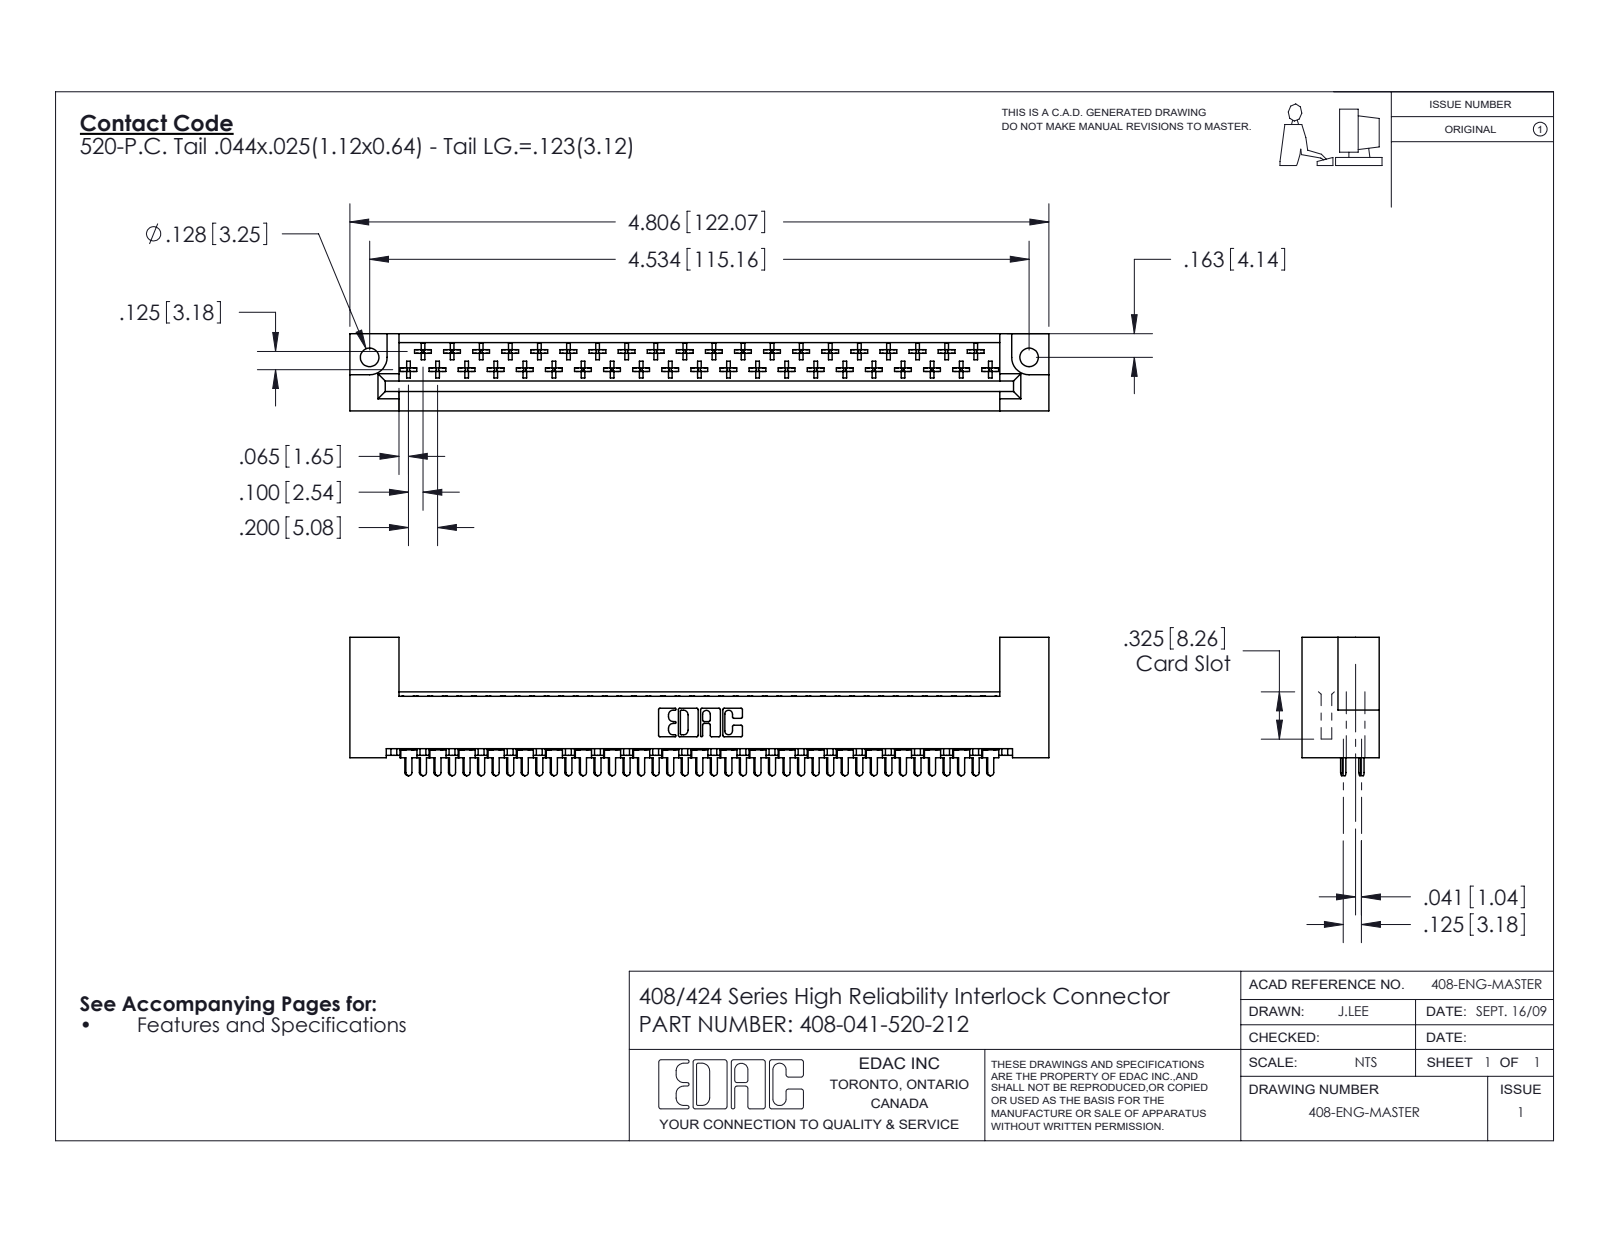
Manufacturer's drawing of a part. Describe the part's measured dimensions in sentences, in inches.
The part is named "408-290-001_408-290-120; 408 Part_041 - 2; 408-041-520-212". Its 3-D file was written by "SolidWorks 2016 (CONFIG_CONTROL_DESIGN)". It is 42 solids with 2394 faces: 1811 planar, 419 cylindrical and 164 other. Overall it measures 4.806 by 0.951 by 0.531 inches. Its volume is 0.916 cubic inches and its surface area 27.13 square inches. Round holes: 2 of diameter 0.128. Partial cylindrical surfaces (rounded edges, fillets, slot ends): 246 of radius 0.01, 43 of radius 0.02, 41 of radius 0.022, 22 of radius 0.01, 6 of radius 0.007, 6 of radius 0.031, 3 of radius 0.026, 2 of radius 0.12. The main face-to-face distances are 0.531, 0.125, 0.1, 0.025, 0.025, 0.361, 0.235, 0.259, 0.398, 0.217. The hole center spacings are 4.534.
